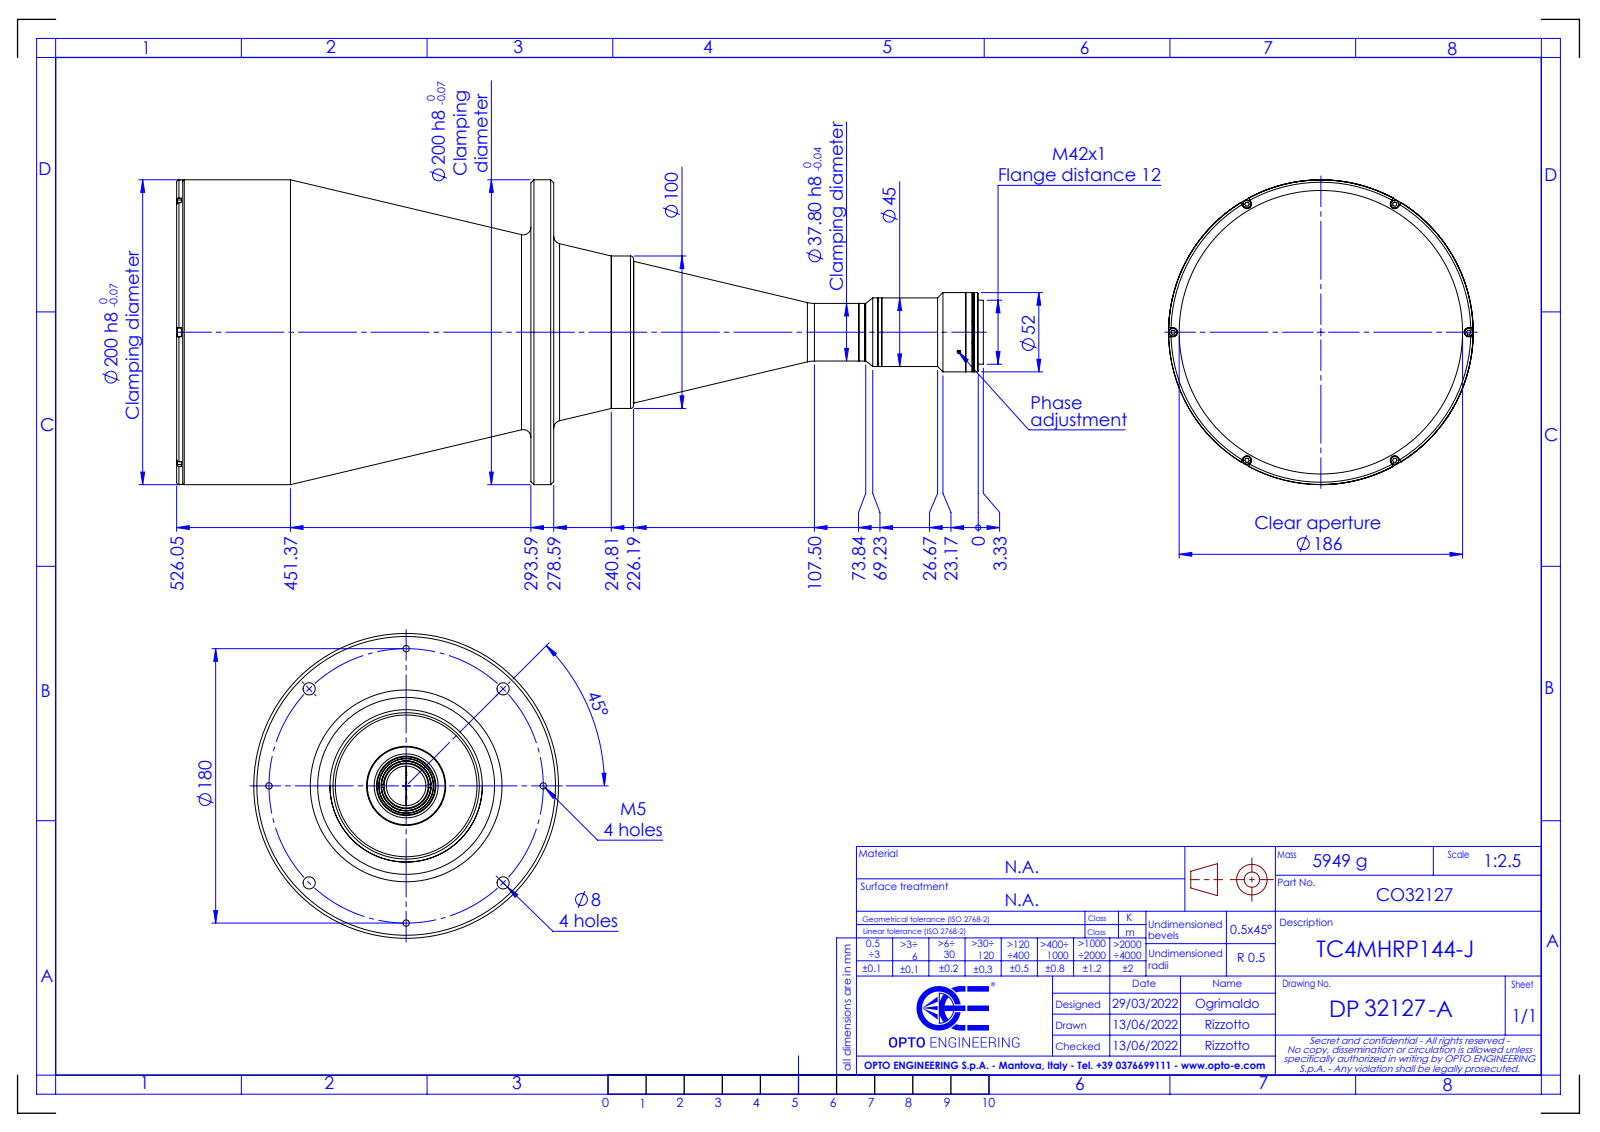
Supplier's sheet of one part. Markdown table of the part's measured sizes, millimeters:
| quantity | value |
| --- | --- |
| part name | DP32127-A_TC4MHRP144-J |
| STEP written by | SolidWorks 2021 (CONFIG_CONTROL_DESIGN) |
| units | millimeters |
| bodies | 0 solids, 196 faces (58 planar, 86 cylindrical, 52 other) |
| overall size | 529.38 × 200 × 200 |
| round holes (diameter × count) | 4.2 × 4, 8 × 4, 2.5 × 3, 38 × 1, 186 × 1, 191.2 × 1 |
| round bosses / shafts (diameter × count) | 5.5 × 6, 200 × 1, 199.8 × 1, 100 × 1, 93 × 1, 52 × 1, 51.8 × 1, 45 × 1 |
| partial cylindrical surfaces (radius × count) | 3 × 4 |
| main face-to-face distances | 15, 232.46, 247.46, 4, 228.46, 243.46, 285.24, 281.24, 52.78, 37.78 |
| hole center spacings | 68.88, 90, 127.28, 166.3, 180 |
